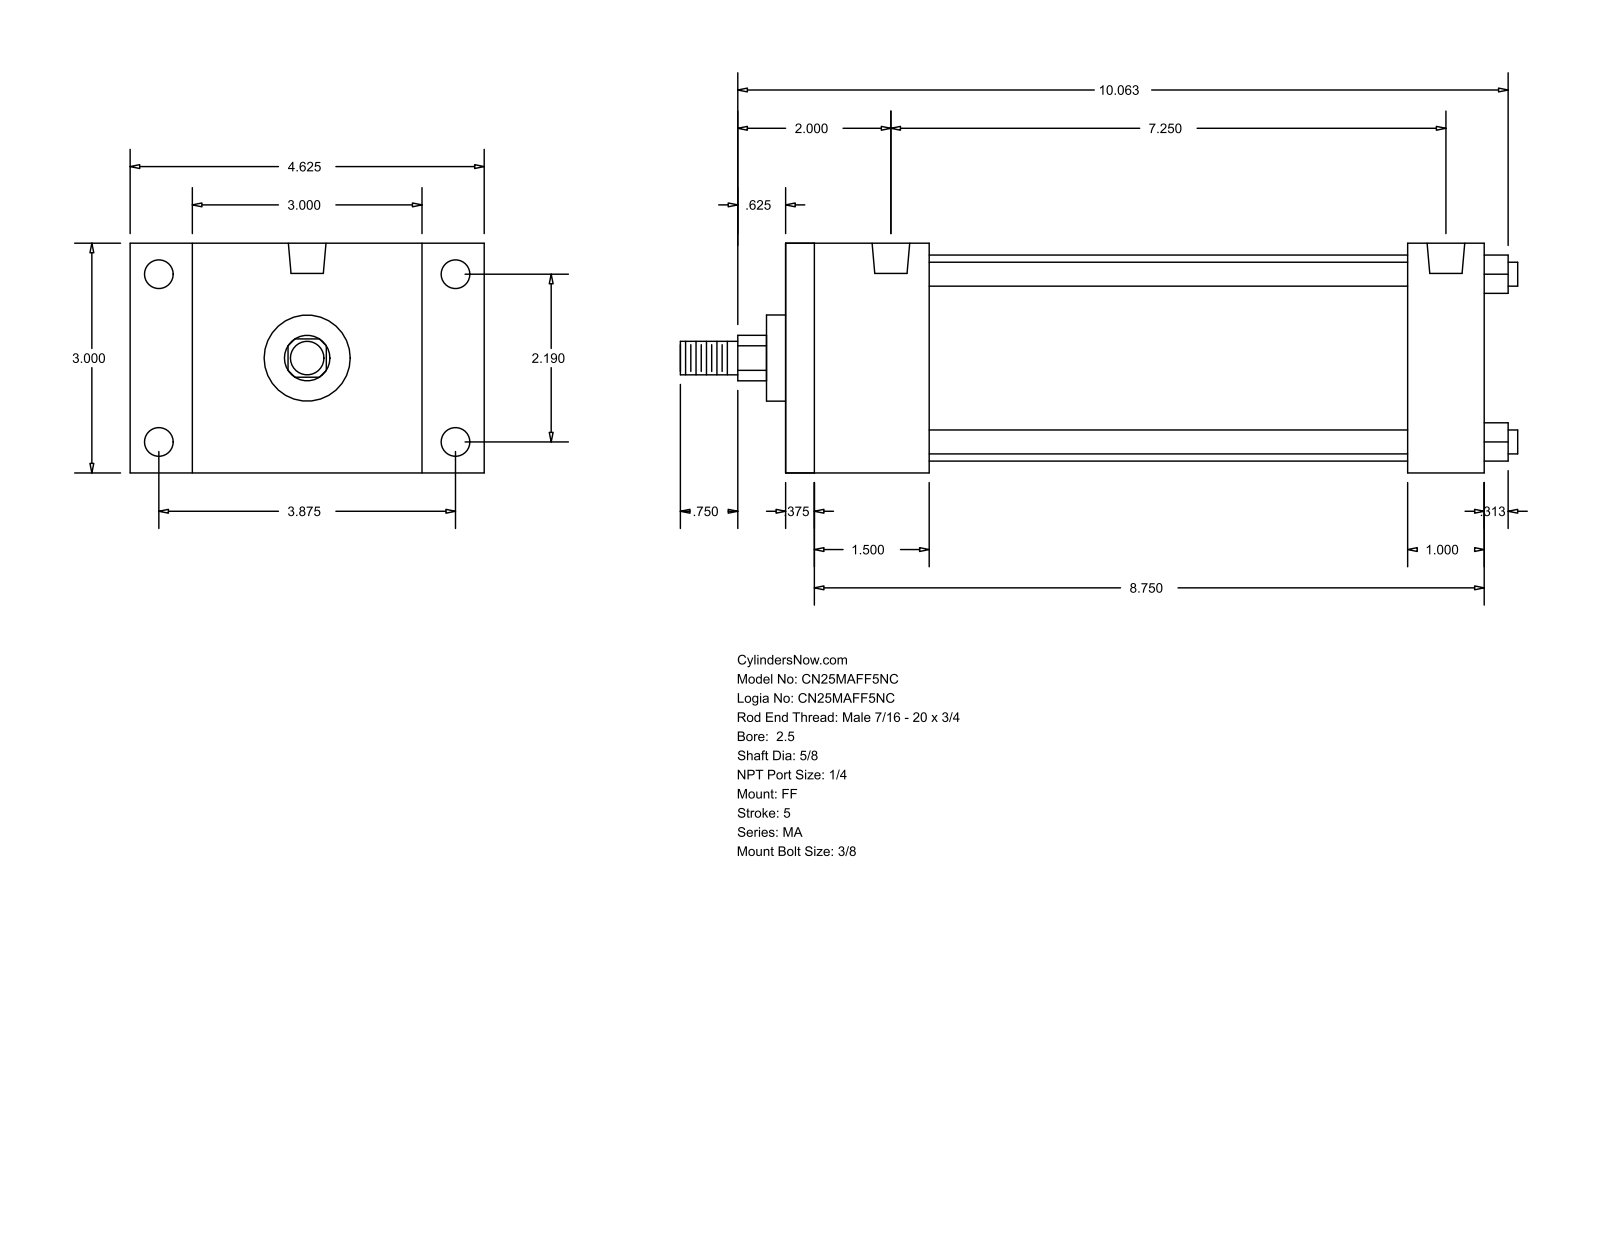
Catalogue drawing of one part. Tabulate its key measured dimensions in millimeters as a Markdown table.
| quantity | value |
| --- | --- |
| part name | MA_FF__0250_0.625 |
| STEP written by | GSSL Pune (CONFIG_CONTROL_DESIGN) |
| units | millimeters |
| bodies | 0 solids, 92 faces (64 planar, 28 cylindrical, 0 other) |
| overall size | 277.81 × 117.47 × 76.2 |
| round holes (diameter × count) | 7.94 × 4, 9.53 × 4, 12.49 × 2 |
| round bosses / shafts (diameter × count) | 7.94 × 4, 68.33 × 1, 28.57 × 1, 15.88 × 1, 11.11 × 1 |
| partial cylindrical surfaces (radius × count) | 7.54 × 1 |
| main face-to-face distances | 76.2, 231.77, 222.25, 9.52, 25.4, 47.62, 206.37, 38.1, 196.85, 158.75 |
| hole center spacings | 55.62, 98.42, 113.05, 184.15 |
